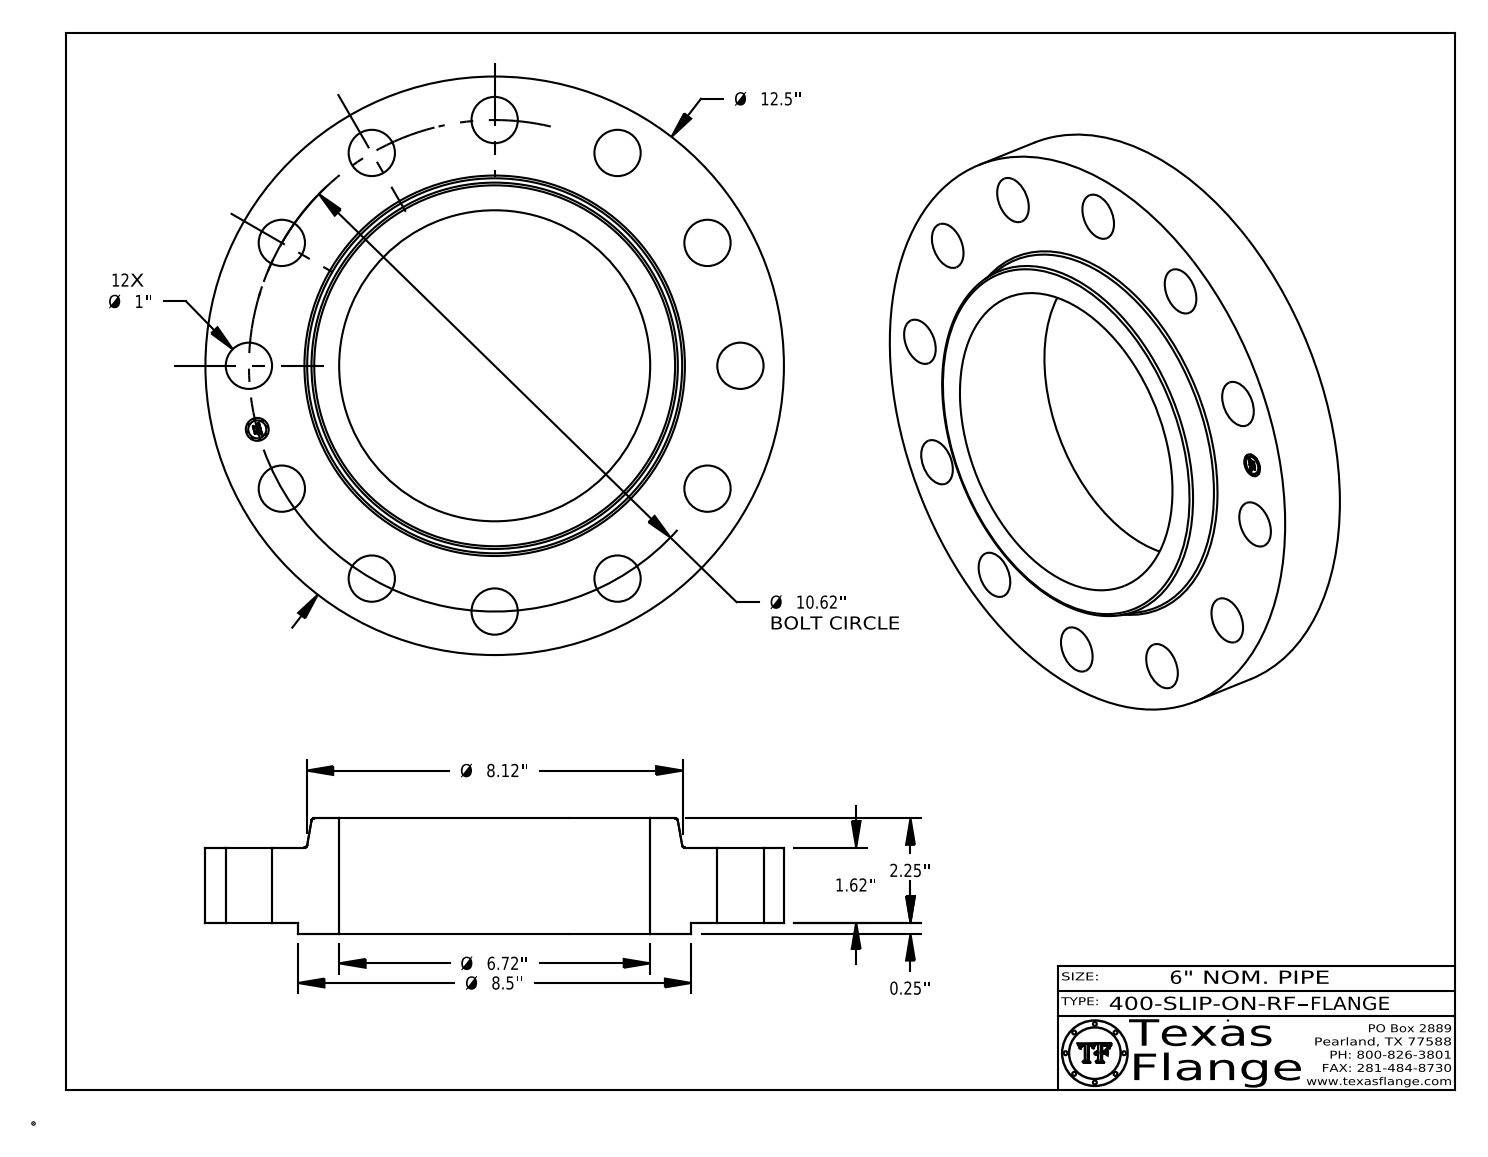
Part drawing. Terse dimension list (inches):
name: 400-SLIP-ON-RF
written by: CATIA V5 STEP AP214 (AUTOMOTIVE_DESIGN)
unit: in
bodies: 1 solid, 425 faces (369 planar, 50 cylindrical, 6 other)
size: 12.5 × 12.5 × 2.5
volume: 140.8 in³; area: 352.3 in²
holes: 12× ⌀1, 1× ⌀0.495, 1× ⌀6.72
bosses: 8× ⌀0.03, 1× ⌀12.5, 1× ⌀8.5, 1× ⌀0.39
face distances: 1.62, 0.25, 1.87, 2.5, 2.25, 0.63, 1.855, 1.605, 0.015, 0.645
hole spacings: 5.31, 10.258, 2.749, 7.509, 9.197, 10.62, 5.31, 2.748
